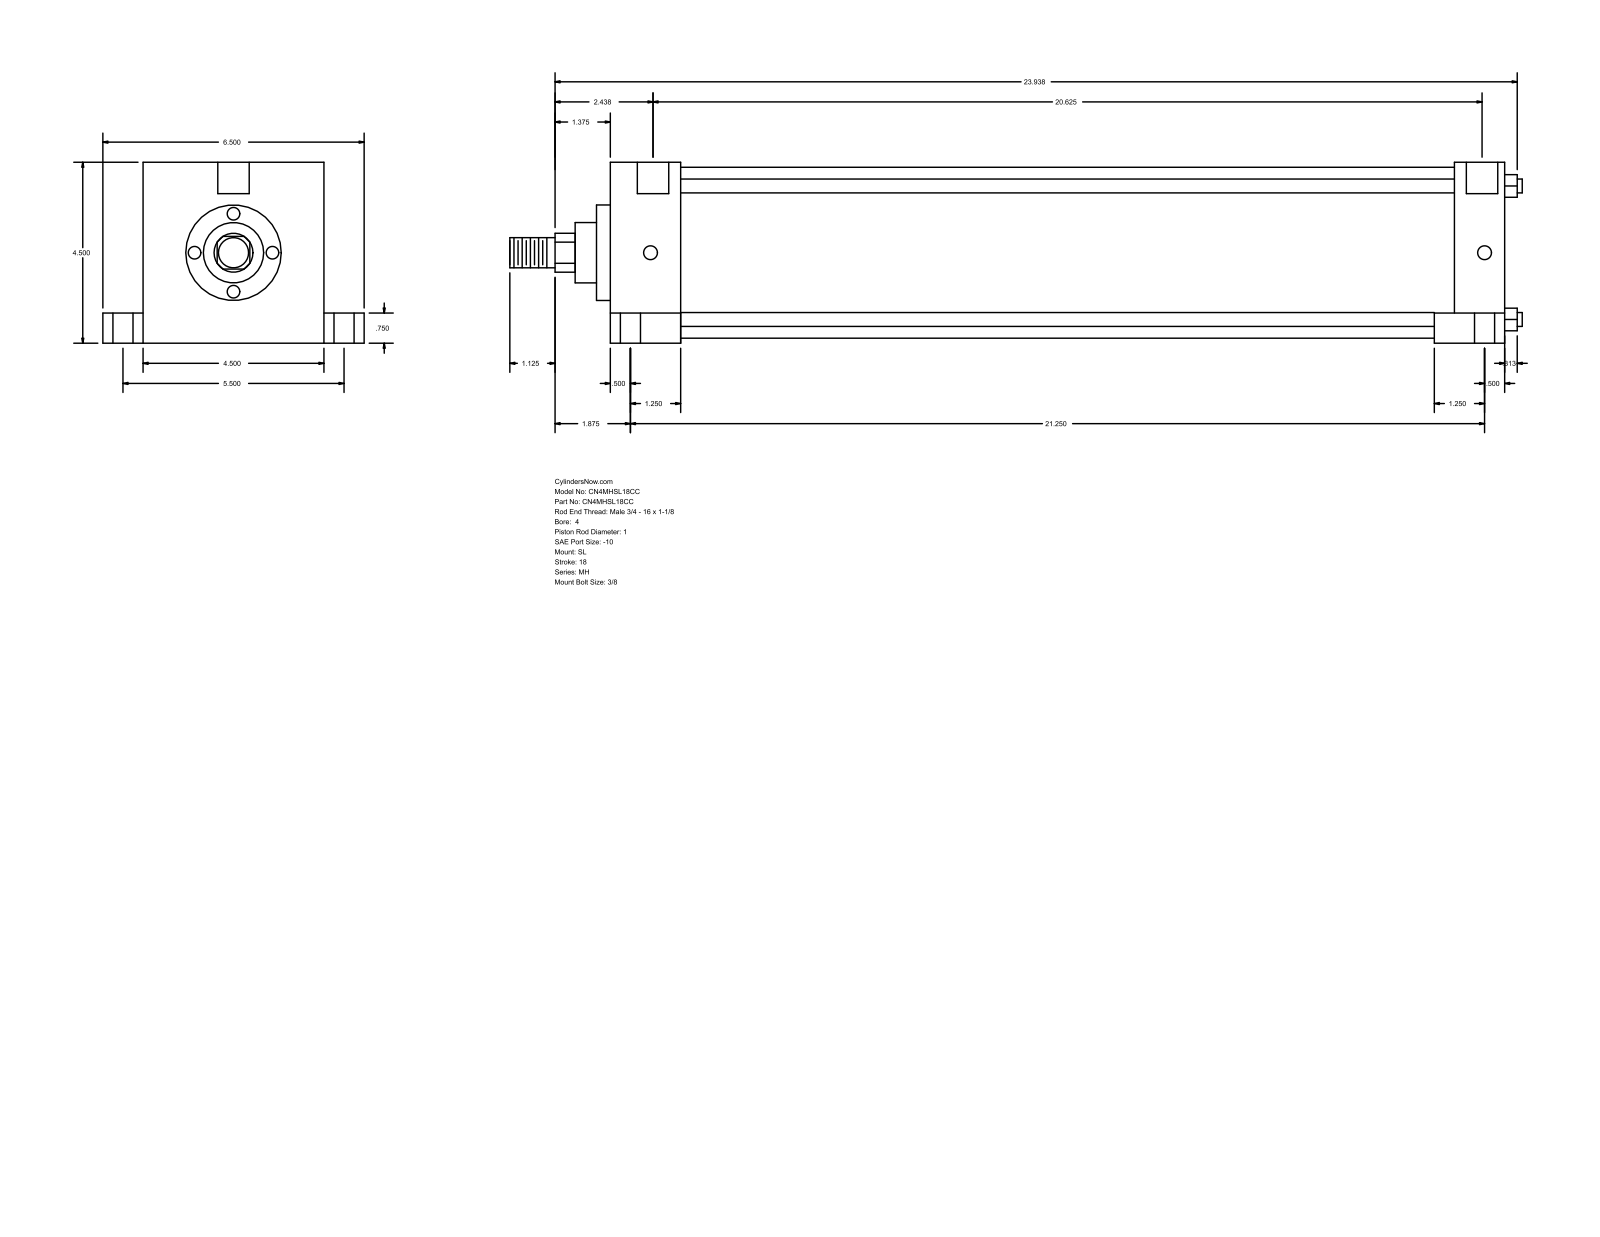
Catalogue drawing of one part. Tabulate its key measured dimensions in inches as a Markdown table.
| quantity | value |
| --- | --- |
| part name | MH_SL__0400_1 |
| STEP written by | GSSL Pune (CONFIG_CONTROL_DESIGN) |
| units | inches |
| bodies | 0 solids, 110 faces (77 planar, 33 cylindrical, 0 other) |
| overall size | 25.187 × 6.5 × 4.5 |
| round holes (diameter × count) | 0.344 × 4, 0.5 × 4, 0.75 × 4, 0.781 × 2 |
| round bosses / shafts (diameter × count) | 0.345 × 4, 4.25 × 1, 2.375 × 1, 1.5 × 1, 1 × 1, 0.75 × 1 |
| partial cylindrical surfaces (radius × count) | 0.484 × 1 |
| main face-to-face distances | 4.5, 22.25, 1.75, 20.5, 21, 19.25, 1.25, 1, 5.5, 0.75 |
| hole center spacings | 2.75, 2.751, 2.795, 2.807, 5.5, 20.75, 20.87, 20.931 |
